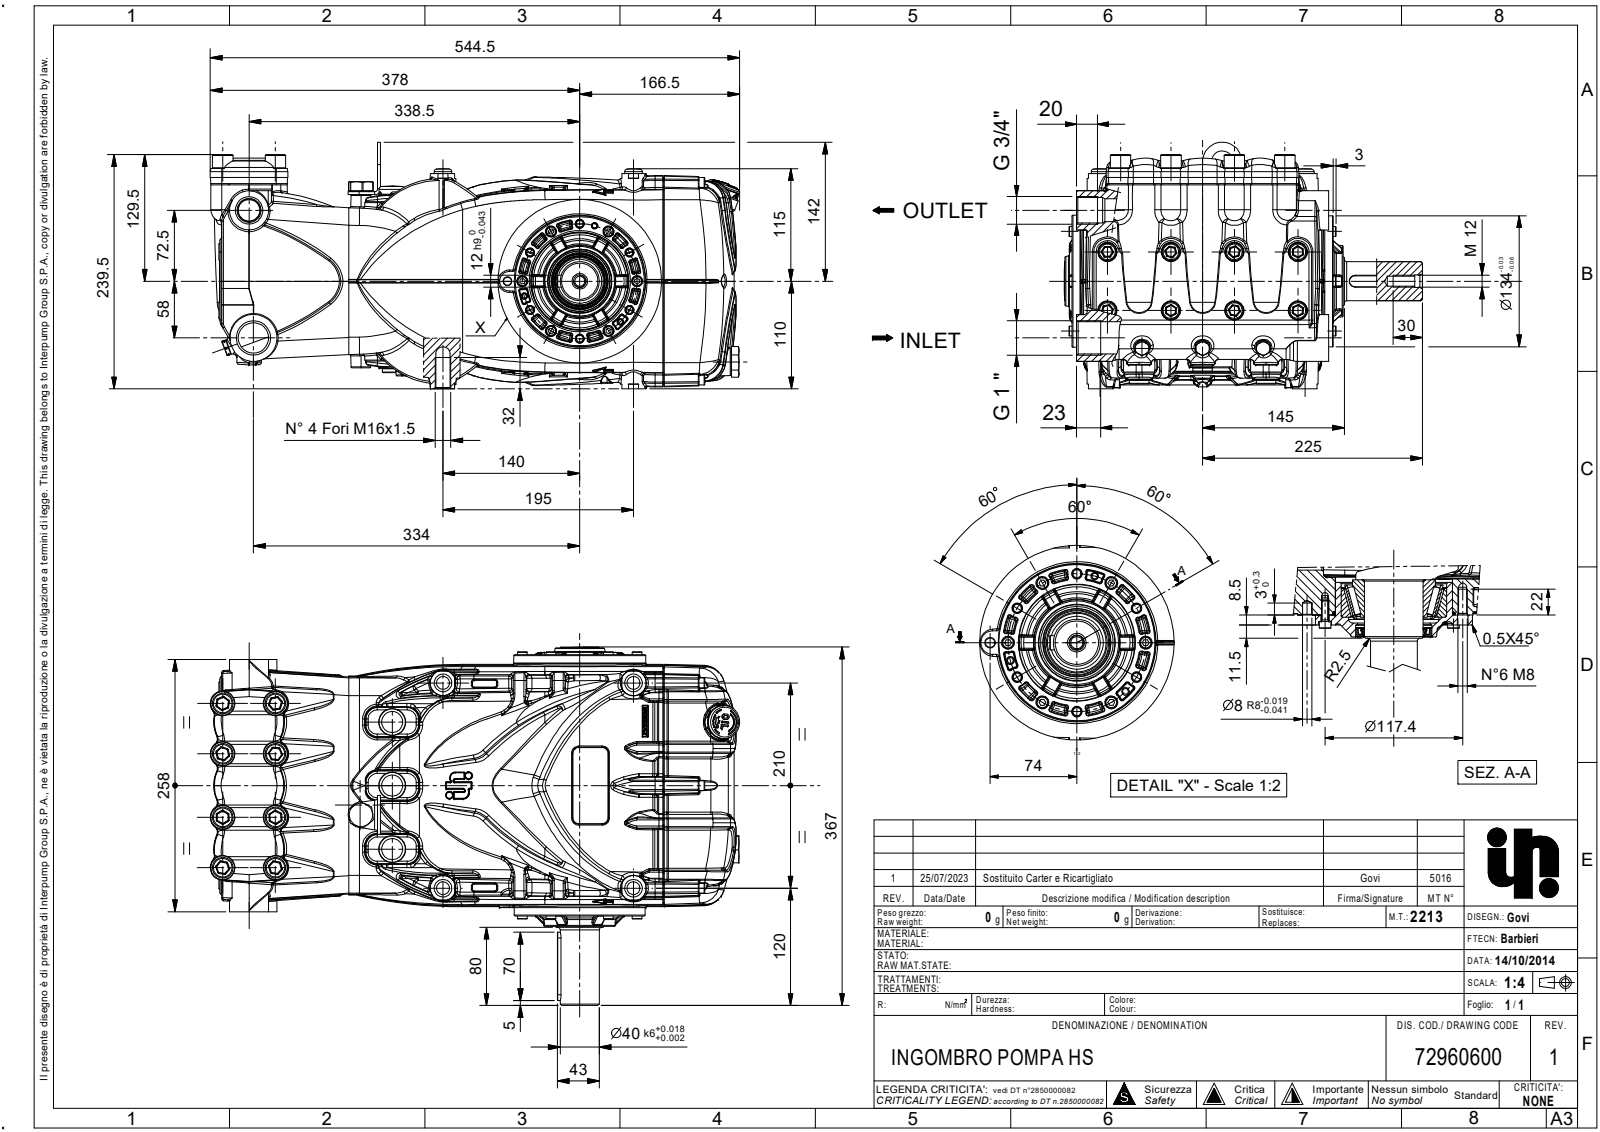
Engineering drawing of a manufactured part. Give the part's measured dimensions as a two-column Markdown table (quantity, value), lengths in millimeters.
| quantity | value |
| --- | --- |
| STEP written by | THINKDESIGN (CONFIG_CONTROL_DESIGN) |
| units | millimeters |
| bodies | 134 solids, 15223 faces (0 planar, 0 cylindrical, 15223 other) |
| overall size | 544.62 × 369.35 × 252.23 |
| volume | 22 150 000 mm³ |
| surface area | 1 380 000 mm² |
